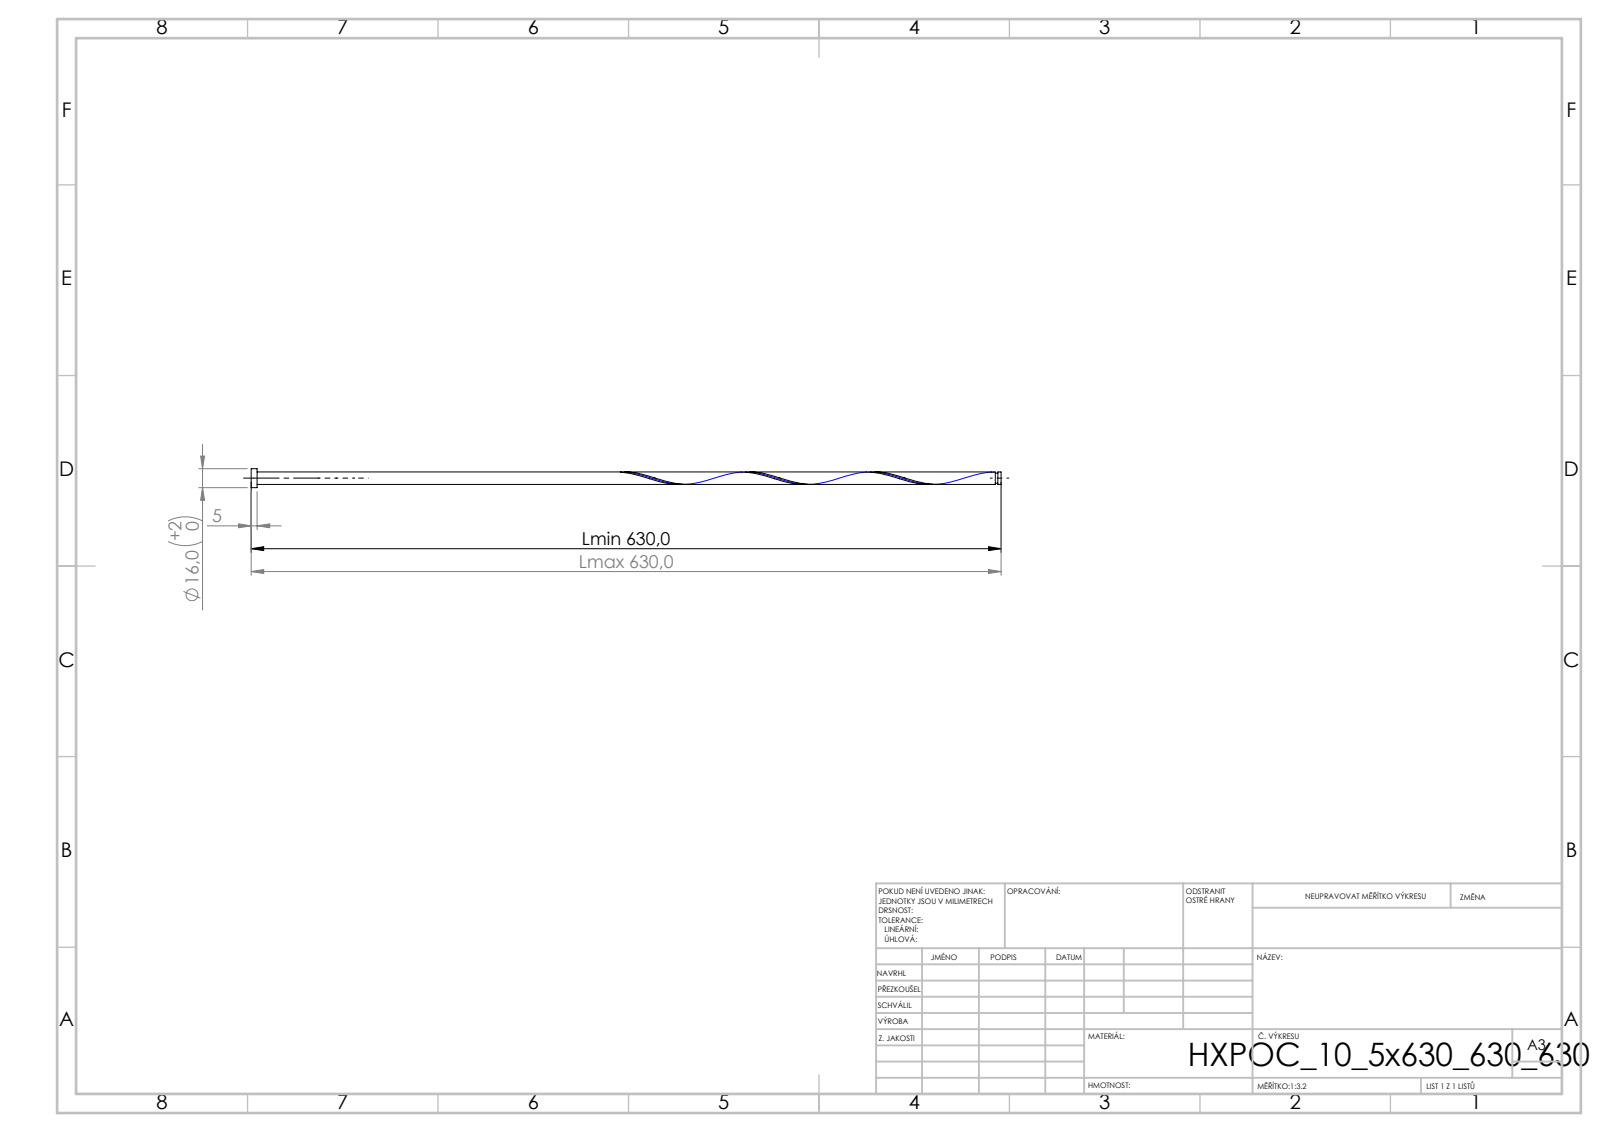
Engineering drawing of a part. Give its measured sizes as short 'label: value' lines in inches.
written by: SolidWorks 2019 (CONFIG_CONTROL_DESIGN)
unit: in
bodies: 1 solid, 16 faces (6 planar, 9 cylindrical, 1 other)
size: 24.803 × 0.63 × 0.63
volume: 4.068 in³; area: 44.29 in²
bosses: 1× ⌀0.63, 1× ⌀0.413, 1× ⌀0.331
face distances: 0.197, 24.803, 24.606, 24.695, 24.498, 0.108, 24.613, 24.416, 0.083, 0.191
